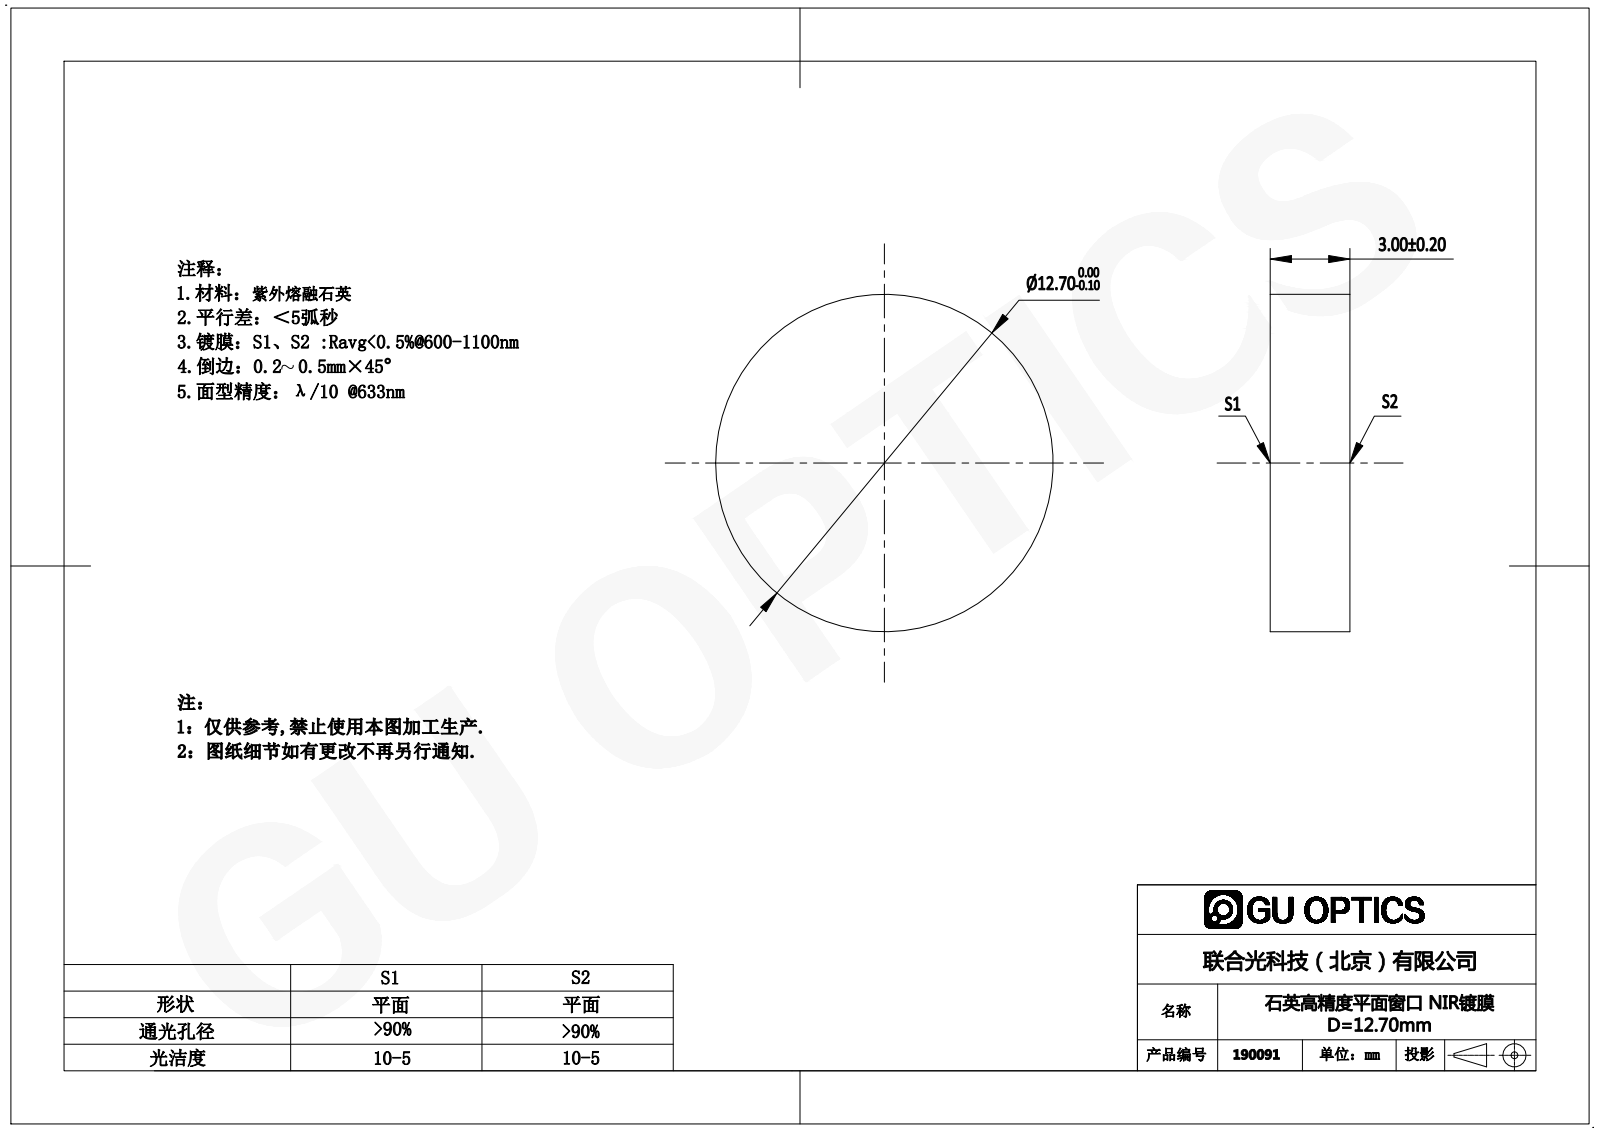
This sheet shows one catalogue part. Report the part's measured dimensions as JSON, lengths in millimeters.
{"part_name": "190058", "step_written_by": "SolidWorks 2016 (AUTOMOTIVE_DESIGN)", "units": "millimeters", "bodies": {"solids": 1, "faces": 4, "planar": 2, "cylindrical": 2, "other": 0}, "overall_size": [12.7, 12.7, 3], "volume_mm3": 380, "surface_area_mm2": 373, "round_bosses_or_shafts": [[12.7, 1]], "face_to_face_distances": [3]}
